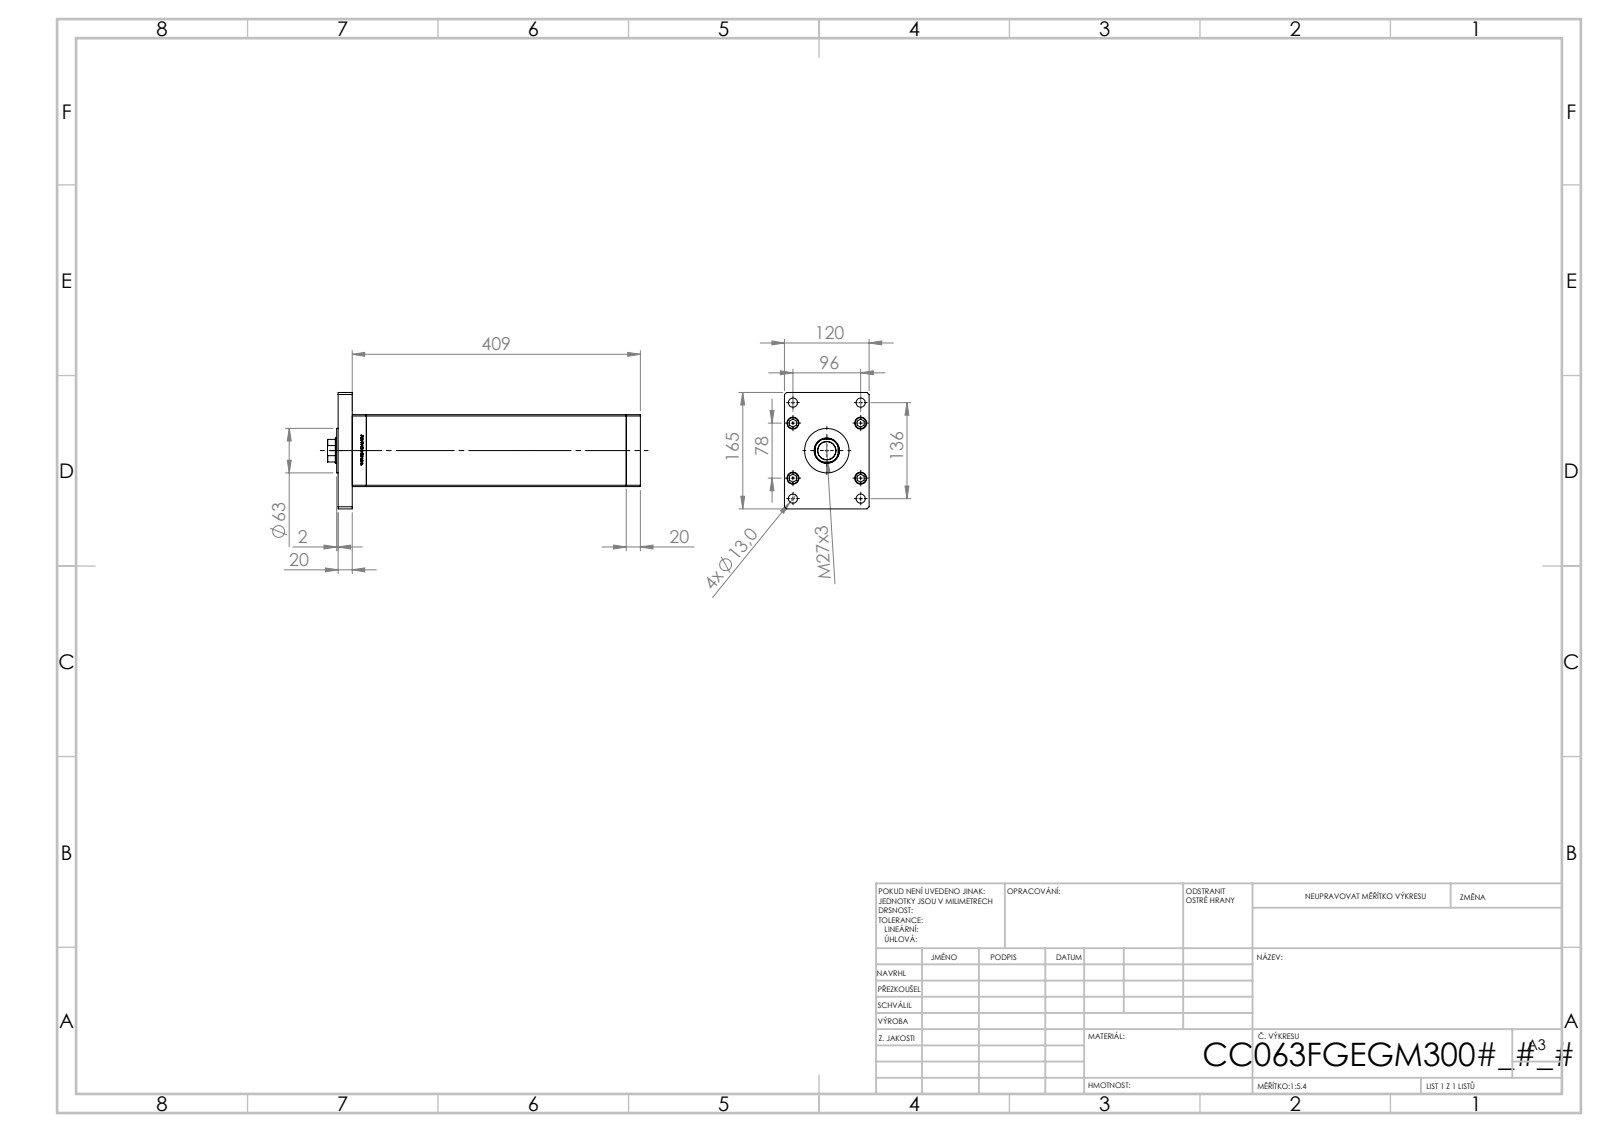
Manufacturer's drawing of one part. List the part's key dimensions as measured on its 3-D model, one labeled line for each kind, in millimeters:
Part name (STEP PRODUCT): V220C_VC_F; V220C_FRONT_F; ALLEN BOLT; V220C_F (+2 more)
STEP written by: SolidWorks 2019 (CONFIG_CONTROL_DESIGN)
Units: millimetres
Bodies: 19 solids, 1311 faces (517 planar, 188 cylindrical, 606 other)
Overall size (bounding box): 443.5 × 165 × 120
Volume: 4 603 000 mm³ · Surface area: 491 786 mm²
Round holes (diameter × count): ⌀13.5 ×5, ⌀18 ×5, ⌀12 ×4, ⌀13 ×4, ⌀17 ×4, ⌀2 ×2, ⌀13.16 ×2, ⌀25.5 ×1, ⌀36 ×1, ⌀37.5 ×1
Round bosses / shafts (diameter × count): ⌀8 ×9, ⌀17 ×5, ⌀63 ×1
Partial cylindrical surfaces — rounded edges, fillets, slot ends (radius × count): R0.93 ×2, R17.5 ×1
Main face-to-face distances: 20, 120, 102, 388.5, 408.5, 368.5, 40, 428.5, 34.25, 42
Hole centre spacings: 41.5, 29, 61.85, 83.23, 96, 100.28, 107, 143.75
